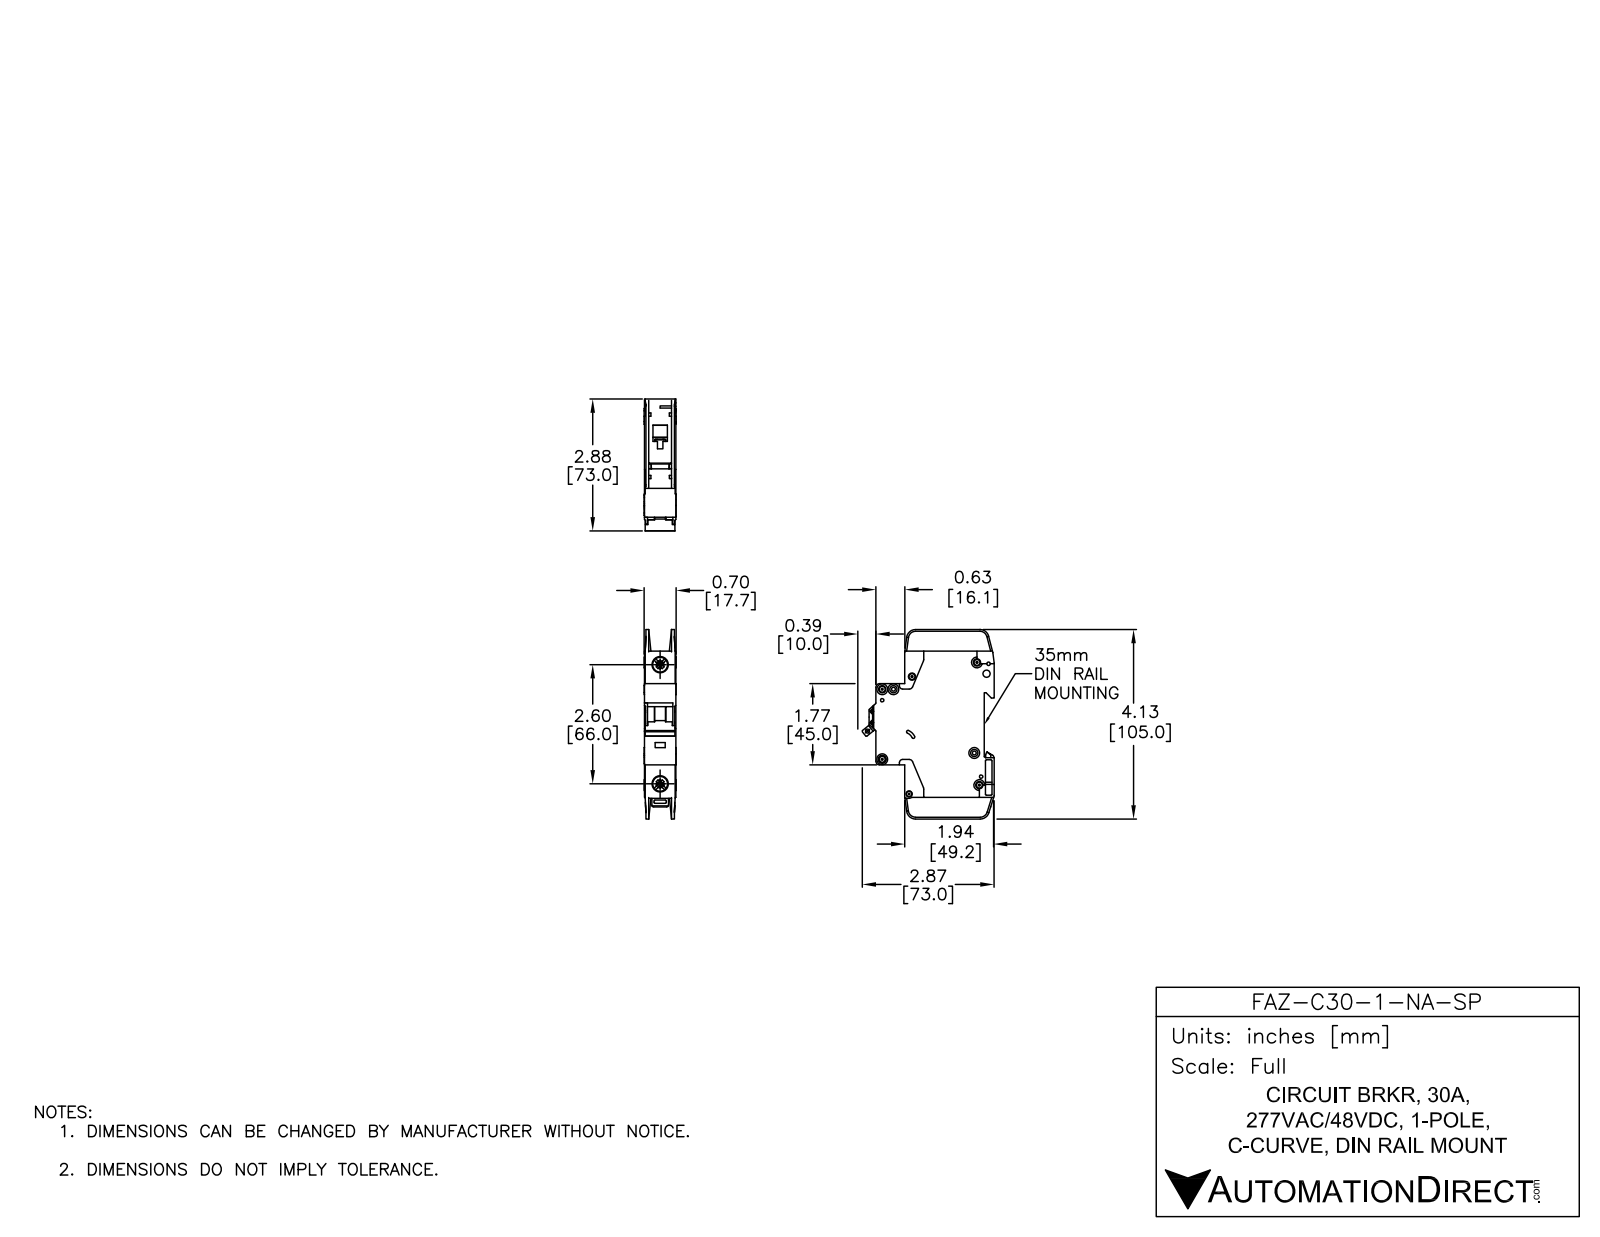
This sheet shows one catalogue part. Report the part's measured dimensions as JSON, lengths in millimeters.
{"part_name": "FAZ-C30-1-NA-SP", "step_written_by": "SolidWorks 2014 (AUTOMOTIVE_DESIGN)", "units": "millimeters", "bodies": {"solids": 3, "faces": 784, "planar": 409, "cylindrical": 263, "other": 112}, "overall_size": [105, 73.04, 17.7], "volume_mm3": 77695, "surface_area_mm2": 24740, "round_holes": [[3.6, 7], [1.09, 2], [1.5, 2], [4, 2], [7.15, 2], [8.2, 2], [1.9, 1], [2.15, 1], [2.2, 1], [2.55, 1], [3.3, 1], [3.4, 1]], "round_bosses_or_shafts": [[6, 7], [2.5, 1]], "partial_cylinders_radius": [[0.25, 29], [0.5, 18], [1, 10], [2, 10], [5, 5], [4, 4], [1.8, 3], [0.2, 2]], "face_to_face_distances": [17.5, 15.05, 0.7, 2.45, 1.75, 15.75, 13.3, 14, 12.6, 2], "hole_center_spacings": [6.2, 5.19, 6.1, 8.19, 8.56, 8.7, 11.11, 12.45]}
